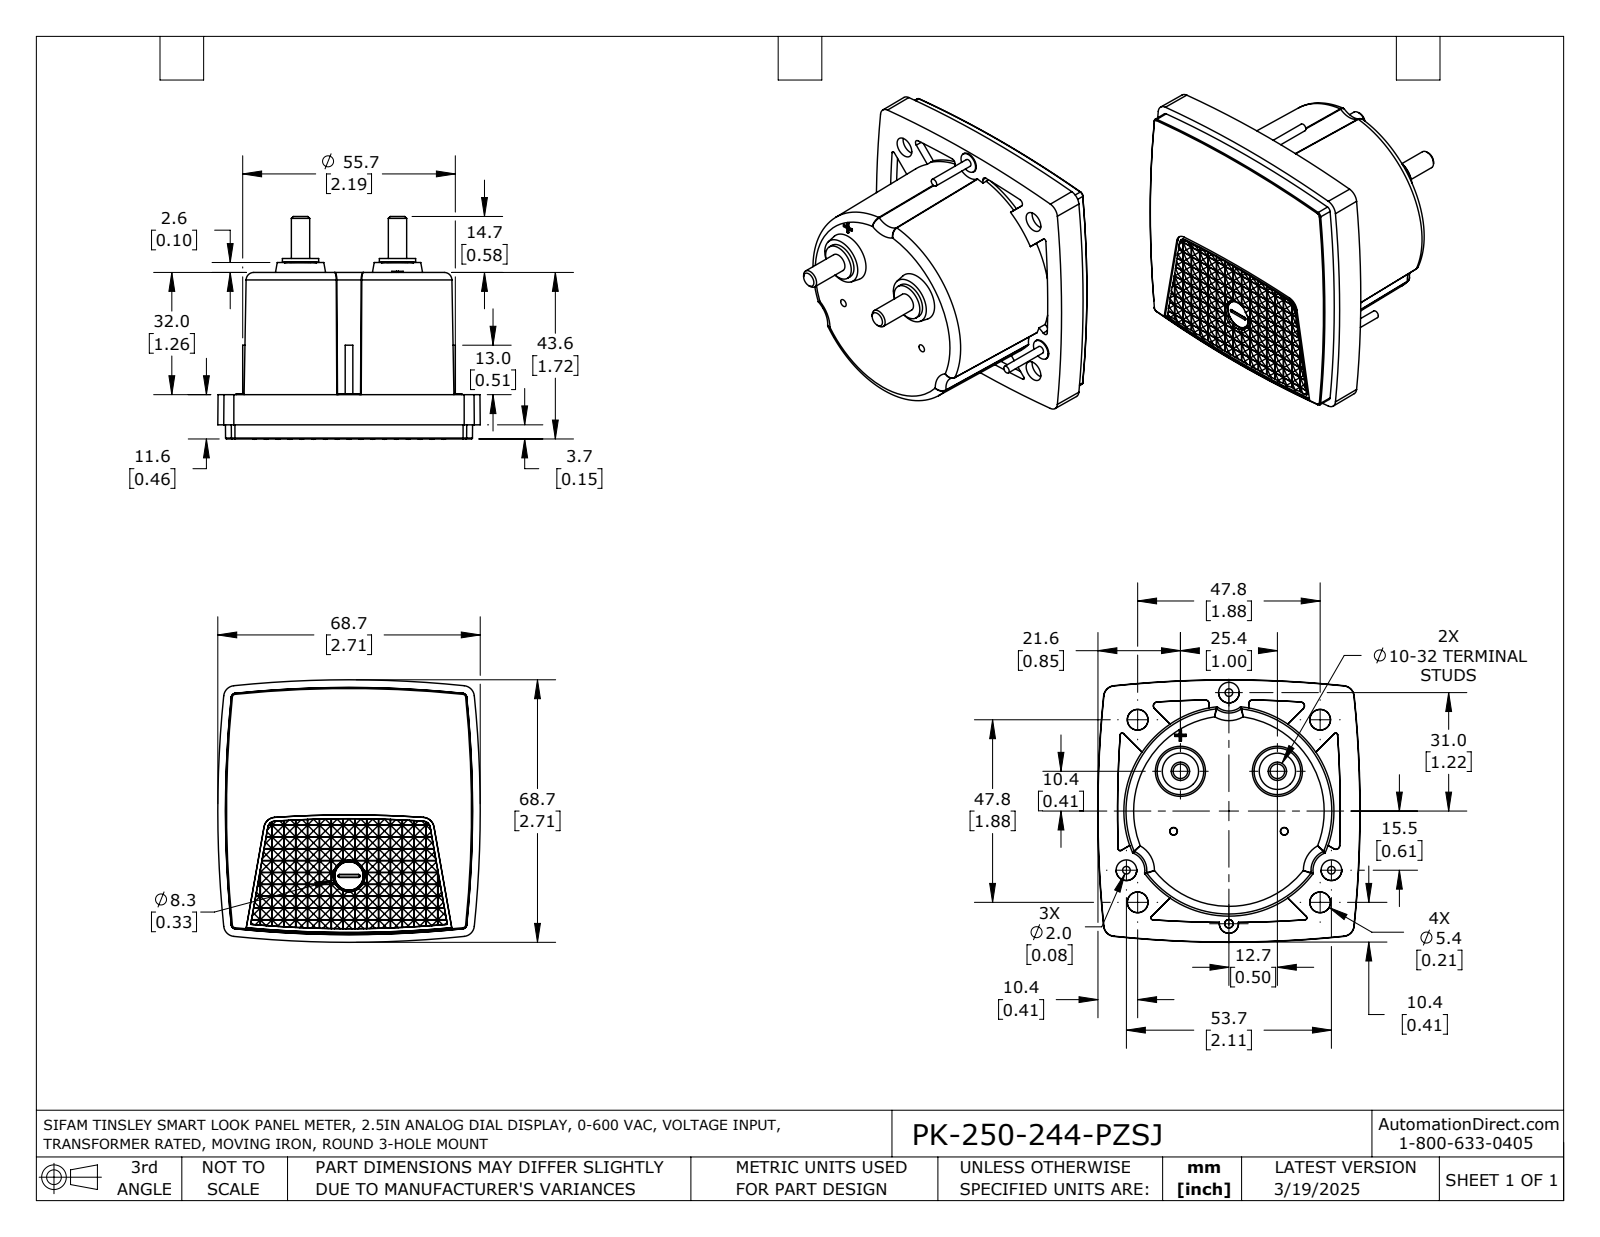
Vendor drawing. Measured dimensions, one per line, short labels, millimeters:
name: PK-250-244-PZSJ
written by: SolidWorks 2021 (AUTOMOTIVE_DESIGN)
unit: mm
bodies: 1 solid, 1550 faces (1165 planar, 265 cylindrical, 120 other)
size: 68.7 × 68.7 × 58.3
volume: 124 400 mm³; area: 19 620 mm²
bosses: 3× ⌀5.4, 3× ⌀2, 2× ⌀9.5, 2× ⌀4.8, 1× ⌀5.5
rounds: 2× R4.2, 1× R27.5
face distances: 43.6, 32, 11.6, 0.6, 2.2, 2.4, 7.9, 3, 1.8, 34.2
